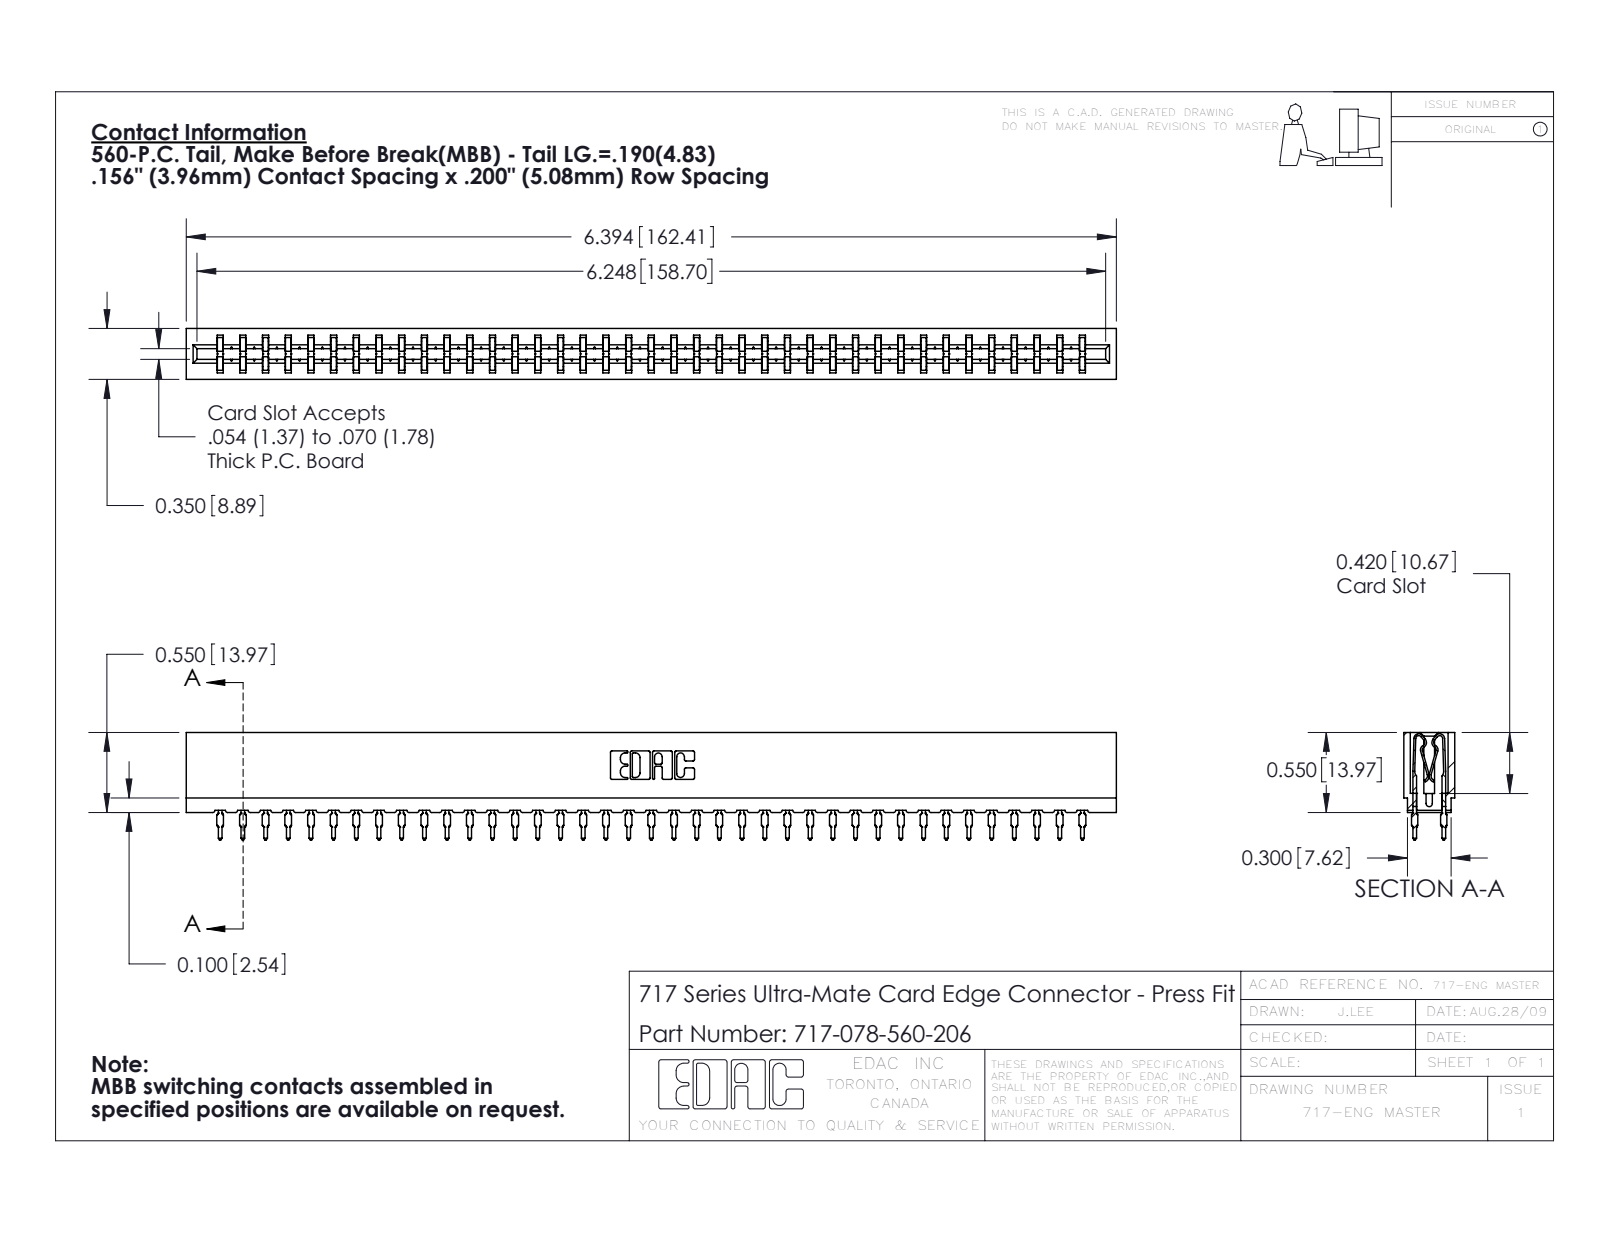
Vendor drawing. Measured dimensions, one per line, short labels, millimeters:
name: 717-078-560-206; 717 Part_Insulator Option - 06; 745-292-001_560
written by: SolidWorks 2016 (CONFIG_CONTROL_DESIGN)
unit: mm
bodies: 79 solids, 7816 faces (4071 planar, 1717 cylindrical, 2028 other)
size: 162.4 × 18.8 × 8.9
volume: 14 400 mm³; area: 23 320 mm²
rounds: 156× R0.5, 78× R0.4, 22× R0.3, 8× R0.1, 8× R0.3, 6× R0.2, 6× R0.8, 3× R0.7
face distances: 5.4, 3.5, 8.9, 1.6, 7.3, 1.9, 3.8, 1.9, 1.1, 7.7
